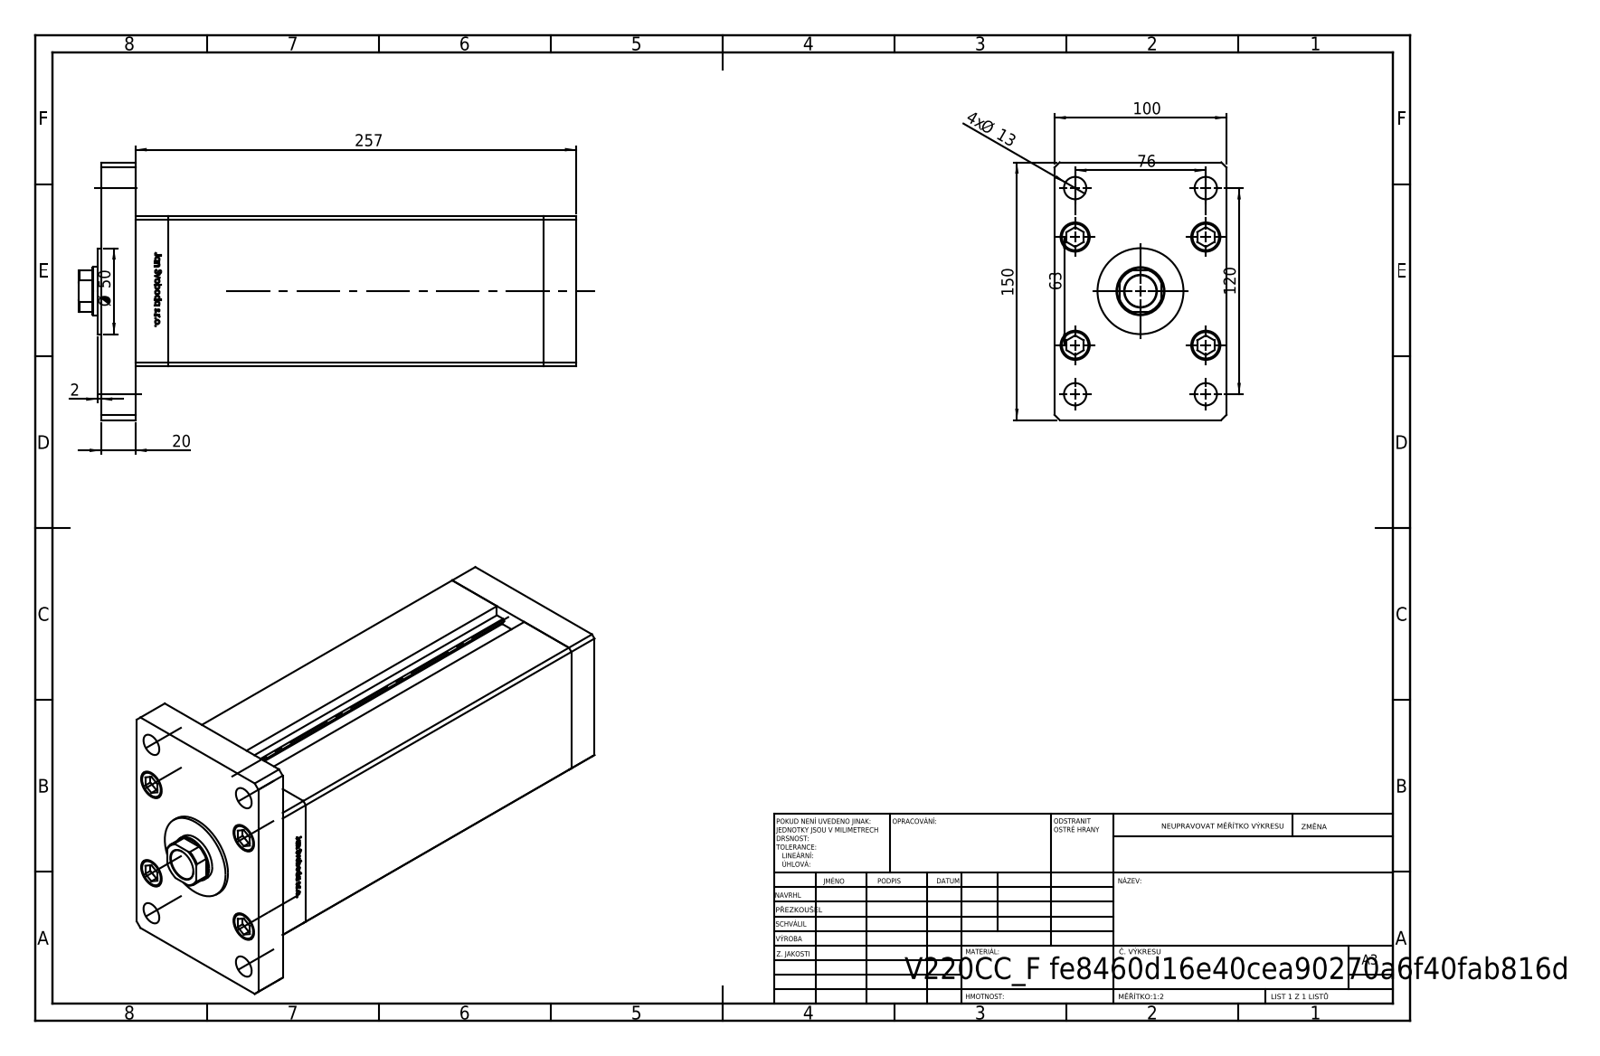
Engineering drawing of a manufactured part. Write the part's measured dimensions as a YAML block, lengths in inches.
part_name: "ALLEN BOLT; V220C_F; V220C_VC_F; V220C_FRONT_F (+2 more)"
step_written_by: "SolidWorks 2019 (CONFIG_CONTROL_DESIGN)"
units: inches
bodies: {solids: 19, faces: 1311, planar: 517, cylindrical: 188, other: 606}
overall_size: [11.398, 5.906, 3.937]
volume: 134.6
surface_area: 471.3
round_holes:
  - {diameter: 0.531, count: 7}
  - {diameter: 0.709, count: 7}
  - {diameter: 0.472, count: 4}
  - {diameter: 0.512, count: 4}
  - {diameter: 0.669, count: 4}
  - {diameter: 0.079, count: 2}
  - {diameter: 0.518, count: 2}
  - {diameter: 0.728, count: 1}
  - {diameter: 1.102, count: 1}
  - {diameter: 1.161, count: 1}
round_bosses_or_shafts:
  - {diameter: 0.315, count: 9}
  - {diameter: 0.669, count: 5}
  - {diameter: 1.969, count: 1}
partial_cylinders:
  - {radius: 0.037, count: 2}
  - {radius: 0.531, count: 1}
face_to_face_distances: [3.937, 3.425, 0.748, 9.35, 0.787, 8.602, 1.535, 10.138, 10.098, 10.886]
hole_center_spacings: [1.339, 0.732, 1.122, 1.462, 1.561, 1.943, 2.281, 2.796]
